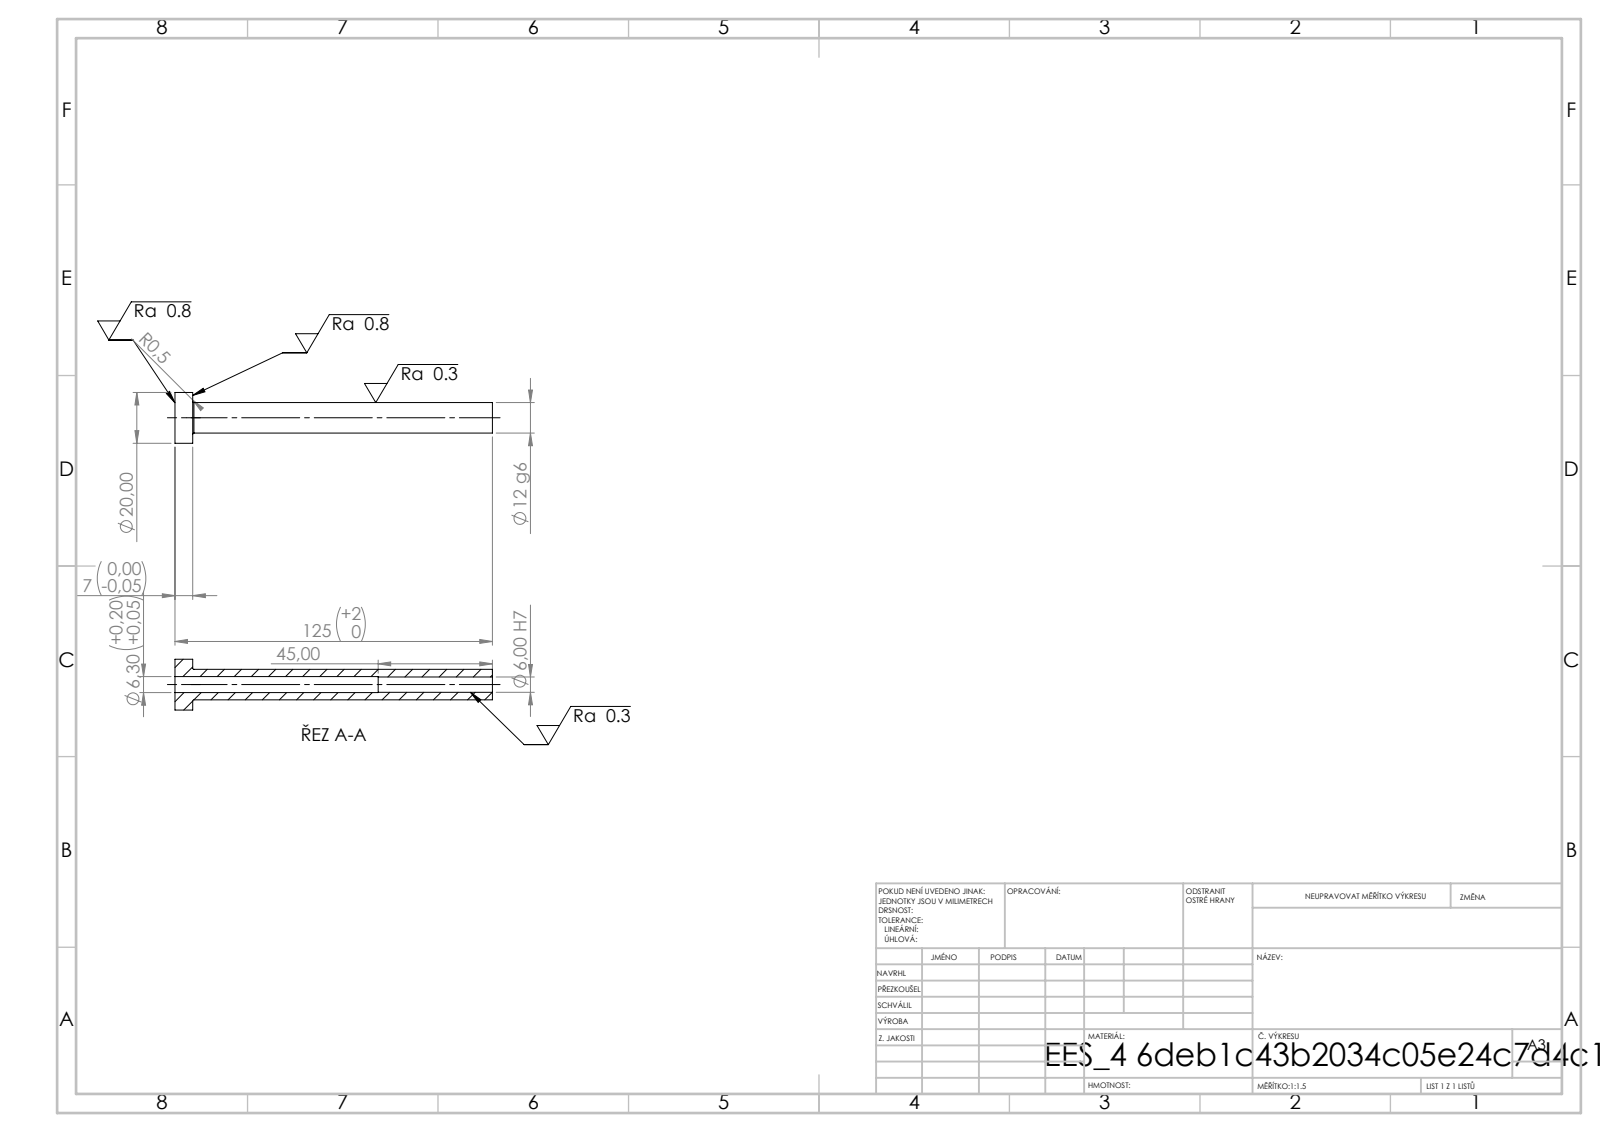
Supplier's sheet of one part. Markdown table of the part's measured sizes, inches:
| quantity | value |
| --- | --- |
| STEP written by | SolidWorks 2019 (CONFIG_CONTROL_DESIGN) |
| units | inches |
| bodies | 1 solid, 14 faces (4 planar, 8 cylindrical, 2 other) |
| overall size | 4.921 × 0.787 × 0.787 |
| volume | 0.719 in³ |
| surface area | 12.22 in² |
| round holes (diameter × count) | 0.236 × 1, 0.248 × 1 |
| round bosses / shafts (diameter × count) | 0.787 × 1, 0.472 × 1 |
| main face-to-face distances | 0.276, 4.921, 4.646, 3.15, 2.874, 1.772 |
